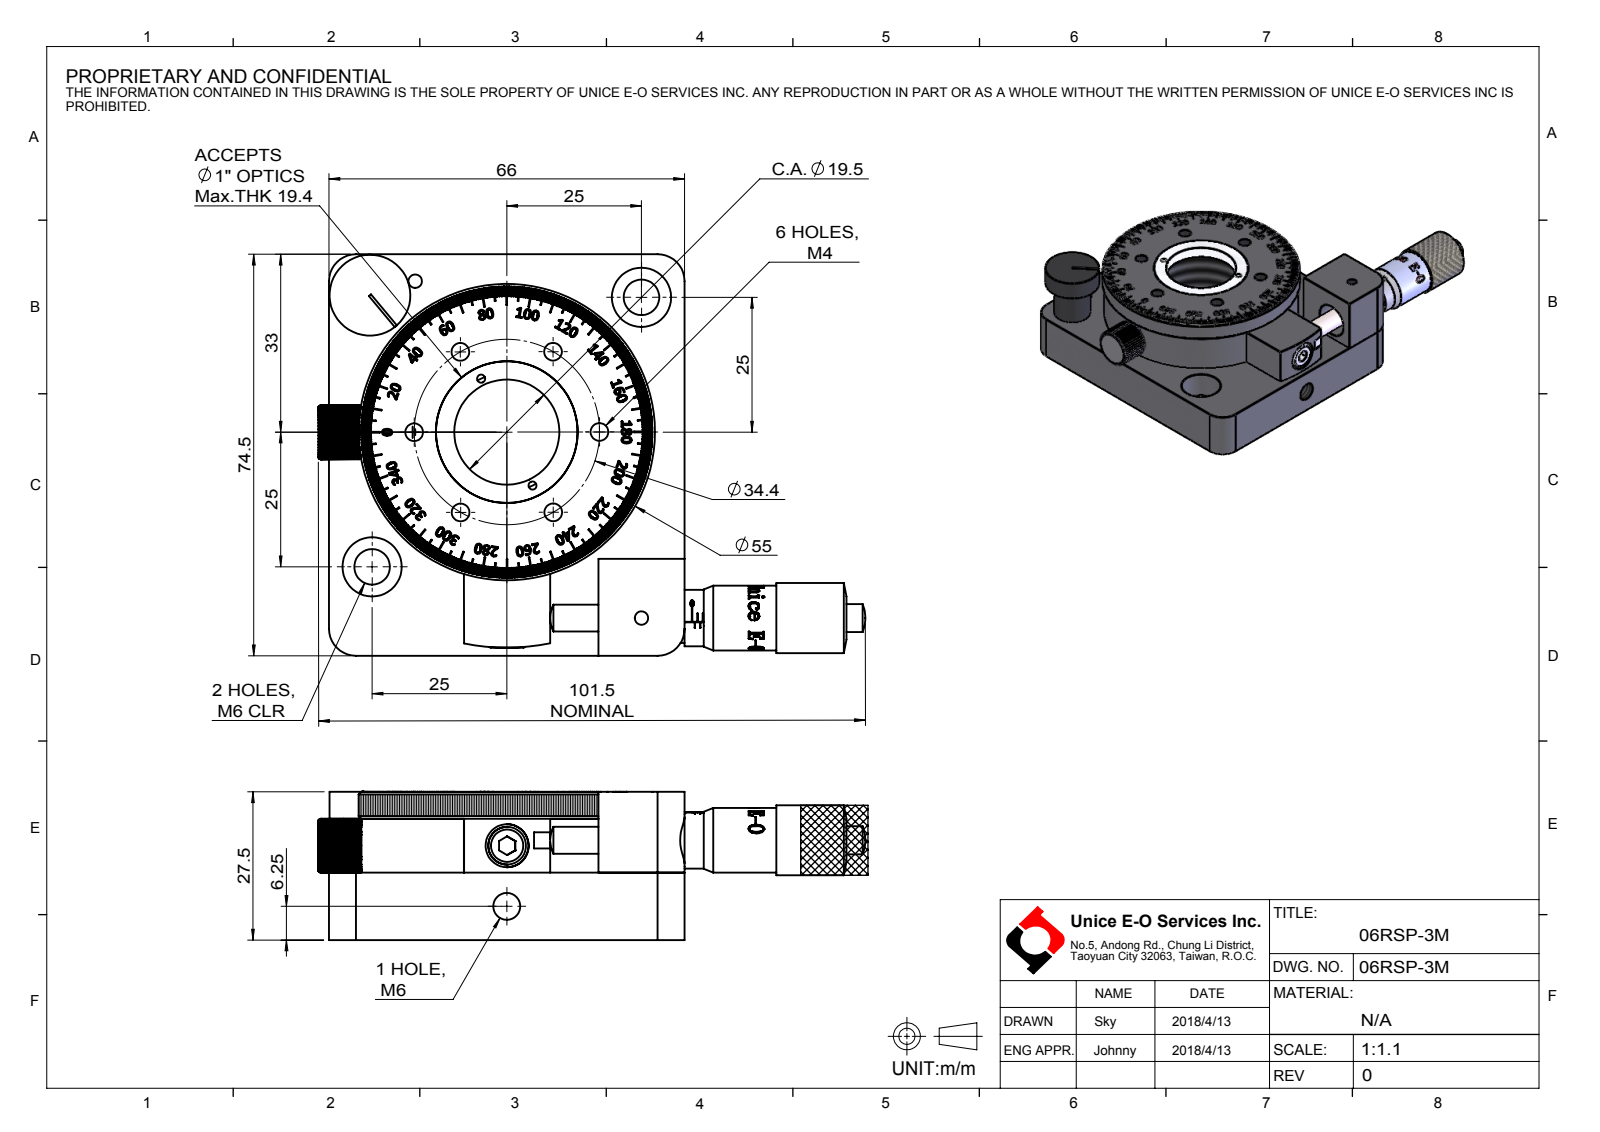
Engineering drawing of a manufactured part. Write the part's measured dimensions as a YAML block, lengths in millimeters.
part_name: "06RSP-3M"
step_written_by: "SolidWorks 2016 (CONFIG_CONTROL_DESIGN)"
units: millimeters
bodies: {solids: 14, faces: 3325, planar: 2395, cylindrical: 270, other: 660}
overall_size: [101.56, 74.5, 27.5]
volume: 88975
surface_area: 41906
round_holes:
  - {diameter: 3.3, count: 9}
  - {diameter: 2.5, count: 7}
  - {diameter: 3.4, count: 5}
  - {diameter: 6.5, count: 5}
  - {diameter: 1.5, count: 2}
  - {diameter: 4.5, count: 2}
  - {diameter: 5, count: 2}
  - {diameter: 6.6, count: 2}
  - {diameter: 8, count: 2}
  - {diameter: 11, count: 2}
  - {diameter: 1.6, count: 1}
  - {diameter: 9.5, count: 1}
round_bosses_or_shafts:
  - {diameter: 4, count: 2}
  - {diameter: 55, count: 1}
  - {diameter: 54, count: 1}
  - {diameter: 47.5, count: 1}
  - {diameter: 25, count: 1}
  - {diameter: 15, count: 1}
  - {diameter: 13, count: 1}
  - {diameter: 12, count: 1}
partial_cylinders:
  - {radius: 5, count: 5}
  - {radius: 1.5, count: 1}
  - {radius: 5.98, count: 1}
  - {radius: 41, count: 1}
face_to_face_distances: [8, 12.5, 4.5, 18, 10, 15, 22.5, 5, 27.5, 23]
hole_center_spacings: [17.2, 29.79, 28.76, 16.63, 16, 33.2, 1.2, 6.2]
